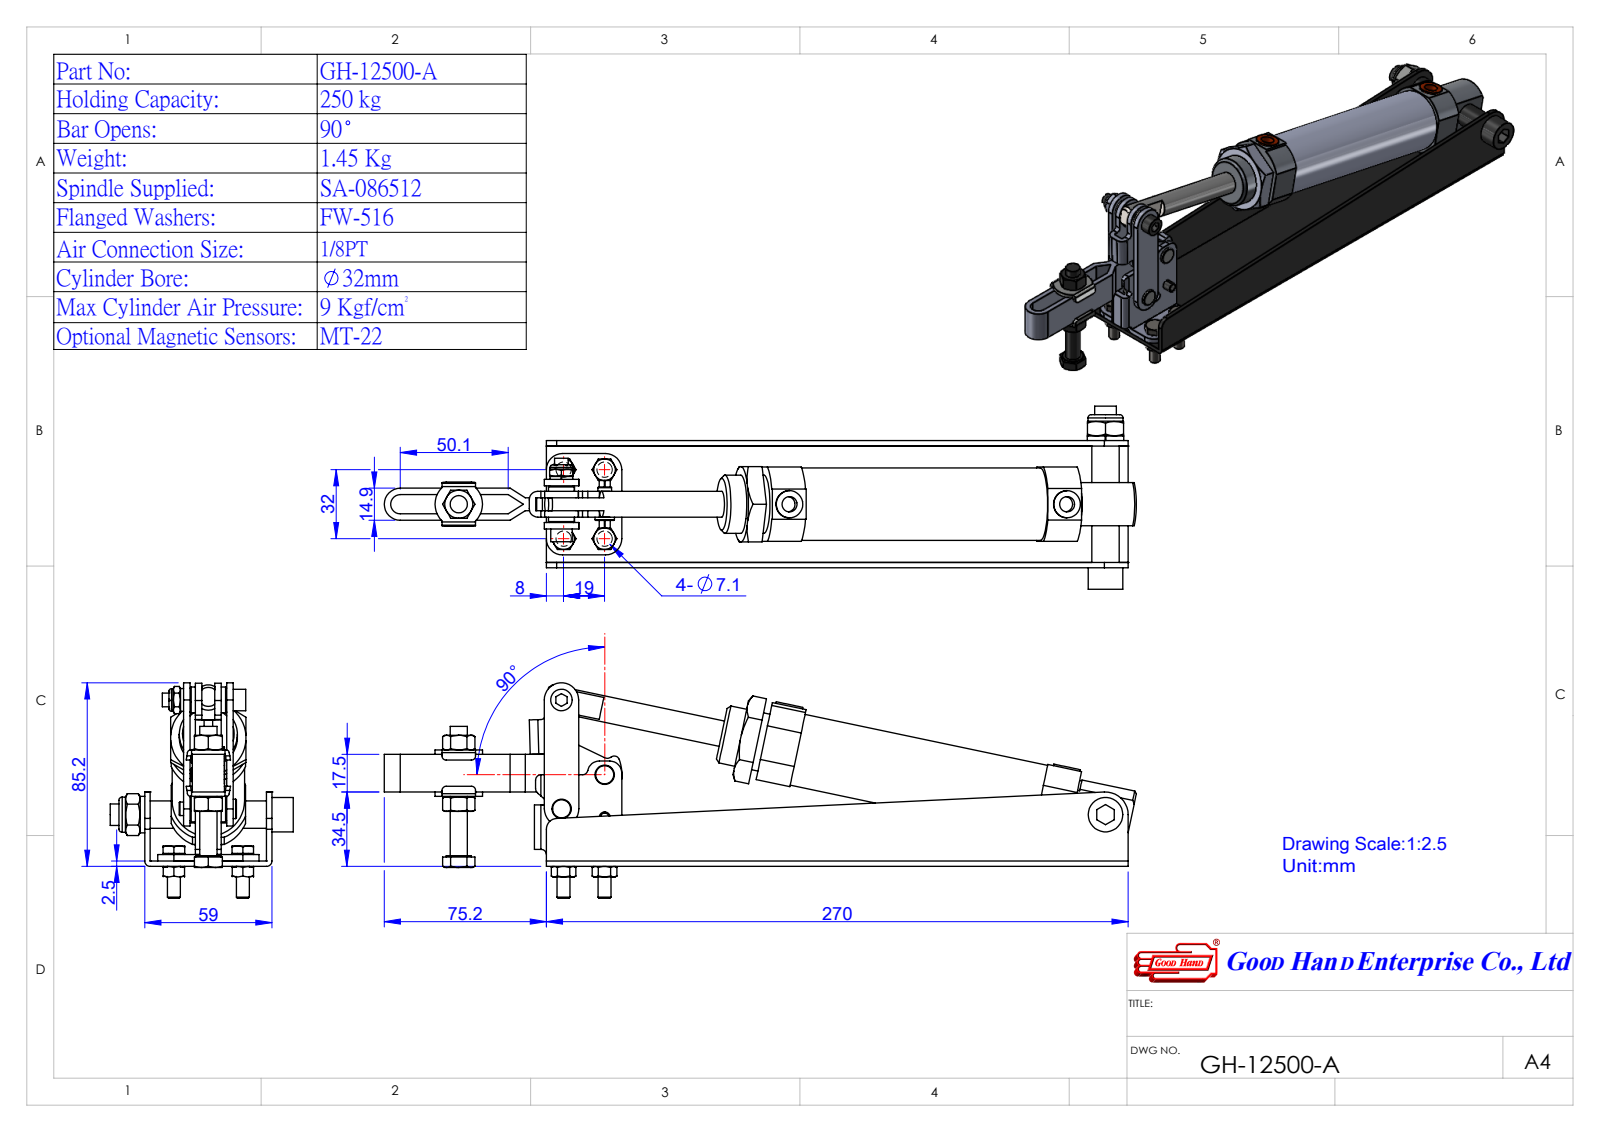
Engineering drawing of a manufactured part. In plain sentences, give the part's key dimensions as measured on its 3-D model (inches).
The part is named "Group7^GH-12500-A(簡化); GH-12500-A(簡化); 112502B08-1^GH-12500-A(簡化); SDA serial cylinder A_SDA 32×75-1^GH-12500-A(簡化) (+4 more)". Its 3-D file was written by "SolidWorks 2016 (AUTOMOTIVE_DESIGN)". It is 7 solids with 652 faces: 302 planar, 231 cylindrical and 119 other. Overall it measures 13.741 by 3.934 by 3.186 inches. Its volume is 15.49 cubic inches and its surface area 224.5 square inches. Round holes: 5 of diameter 0.197, 2 of diameter 0.28, 1 of diameter 0.161, 1 of diameter 0.26, 1 of diameter 0.283, 1 of diameter 0.416, 1 of diameter 0.472, 1 of diameter 0.5, 1 of diameter 1.181. Round bosses or shafts: 6 of diameter 0.394, 4 of diameter 0.236, 3 of diameter 0.354, 3 of diameter 0.25, 2 of diameter 0.496, 1 of diameter 1.323, 1 of diameter 1.181, 1 of diameter 1.063. Partial cylindrical surfaces (rounded edges, fillets, slot ends): 6 of radius 0.079, 5 of radius 0.059, 4 of radius 0.295, 3 of radius 0.016, 3 of radius 0.118, 2 of radius 0.039, 2 of radius 0.098, 2 of radius 0.099. The main face-to-face distances are 0.098, 2.224, 0.118, 2.126, 2.323, 1.28, 1.181, 1.043, 0.945, 1.398. The hole center spacings are 0.355, 0.606, 0.78, 0.803, 0.833, 0.958, 1.004, 1.02.
